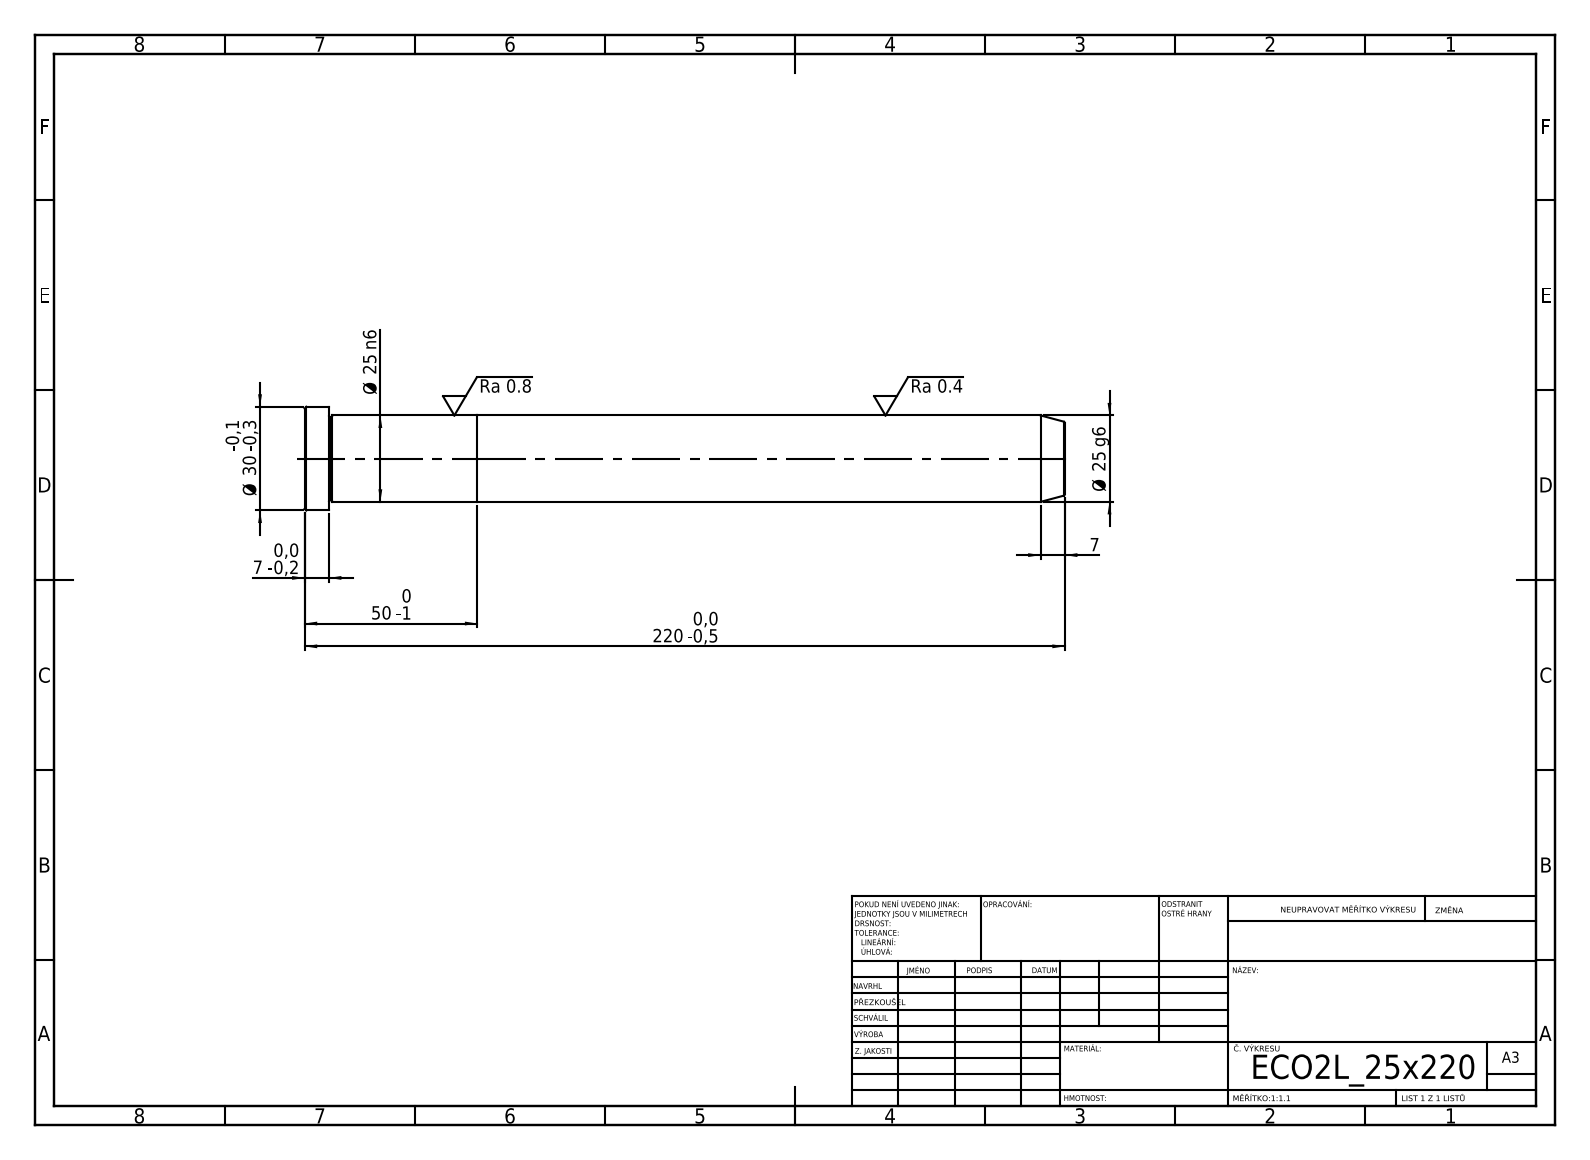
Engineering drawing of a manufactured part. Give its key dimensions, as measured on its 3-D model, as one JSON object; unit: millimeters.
{"step_written_by": "SolidWorks 2019 (CONFIG_CONTROL_DESIGN)", "units": "millimeters", "bodies": {"solids": 2, "faces": 21, "planar": 5, "cylindrical": 6, "other": 10}, "overall_size": [220, 30, 30], "volume_mm3": 108970, "surface_area_mm2": 19631, "round_bosses_or_shafts": [[30, 1], [25, 1]], "face_to_face_distances": [50, 170, 220, 213, 43, 7]}
